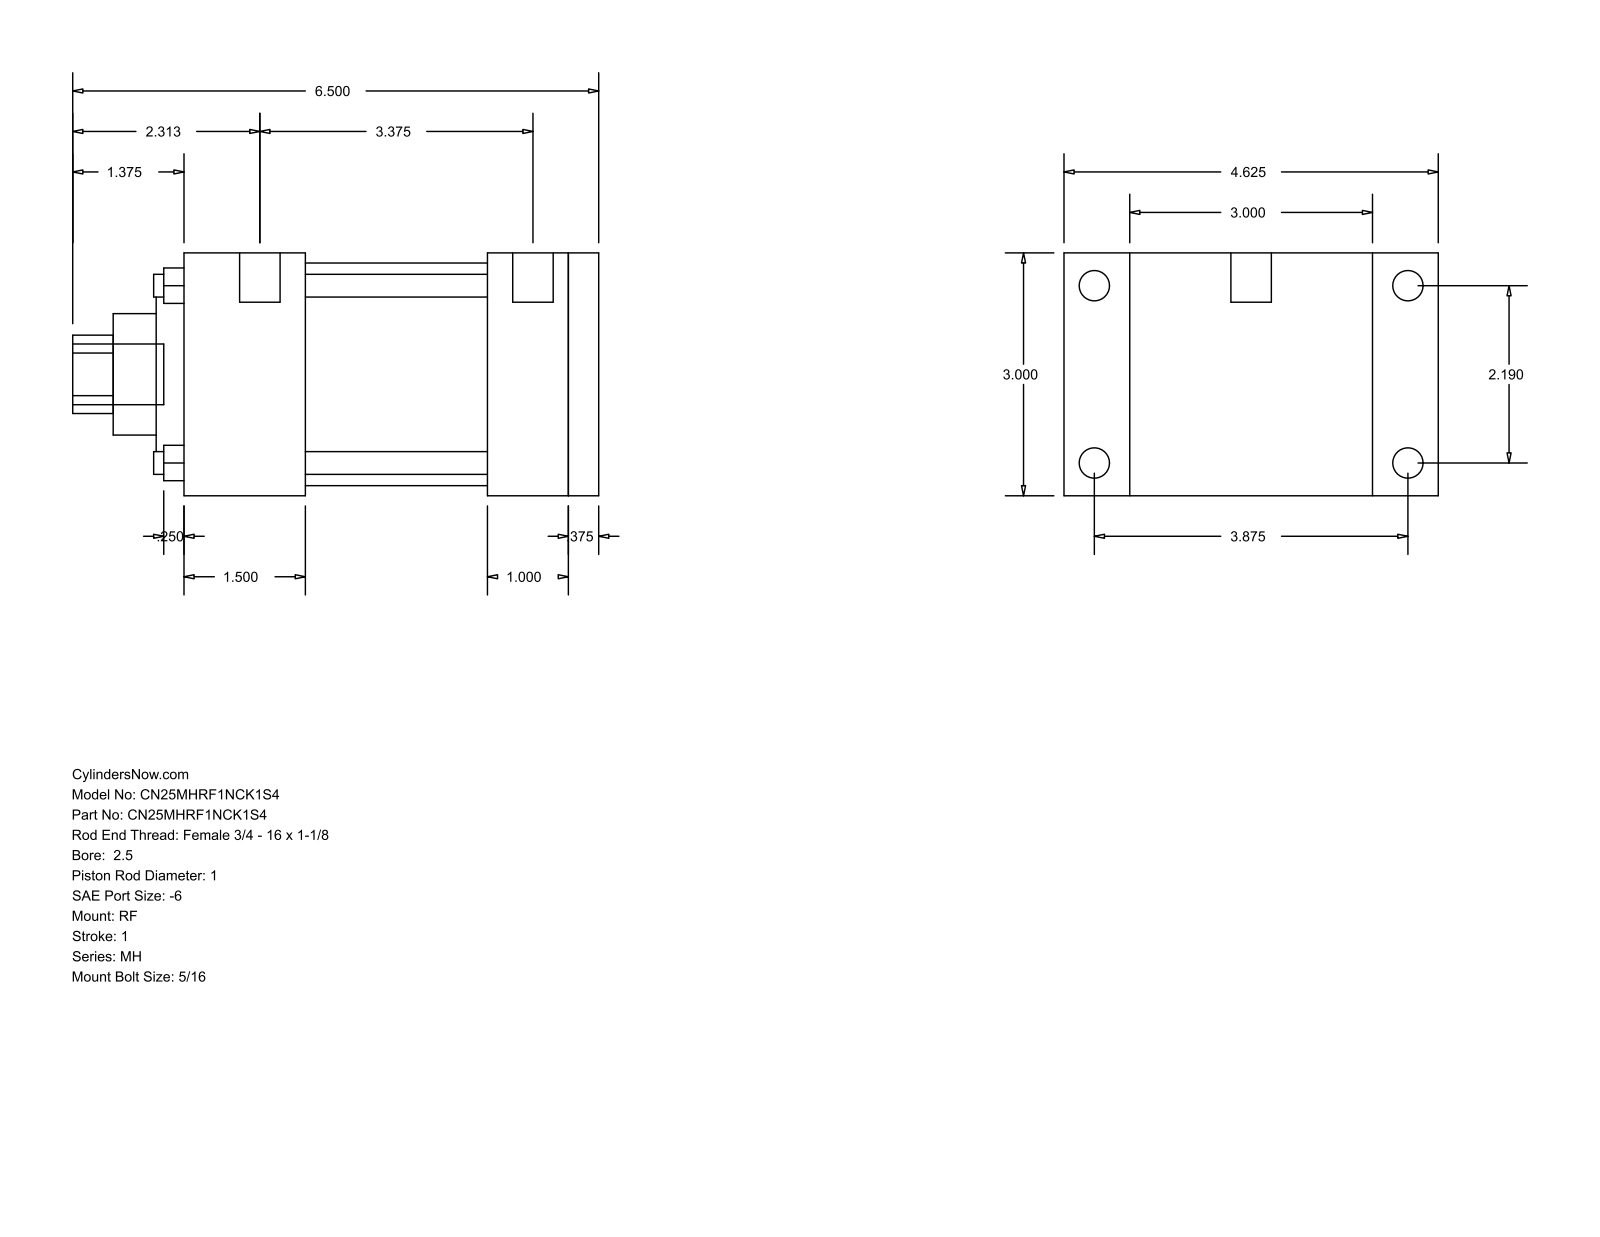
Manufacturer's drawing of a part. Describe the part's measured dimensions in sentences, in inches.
The part is named "MH_RF__0250_1". Its 3-D file was written by "GSSL Pune (CONFIG_CONTROL_DESIGN)". It is 0 solids with 94 faces: 65 planar, 29 cylindrical and 0 other. Overall it measures 6.5 by 4.625 by 3 inches. Round holes: 4 of diameter 0.281, 1 of diameter 1, 1 of diameter 1.5, 1 of diameter 2.375, 1 of diameter 2.75. Round bosses or shafts: 4 of diameter 0.375, 4 of diameter 0.219, 2 of diameter 0.5, 1 of diameter 0.75. Partial cylindrical surfaces (rounded edges, fillets, slot ends): 1 of radius 0.484. The main face-to-face distances are 3, 0.375, 5.125, 4.75, 1.375, 1, 3.75, 1.5, 2.25, 3.25. The hole center spacings are 1.548, 2.19, 3.097.
